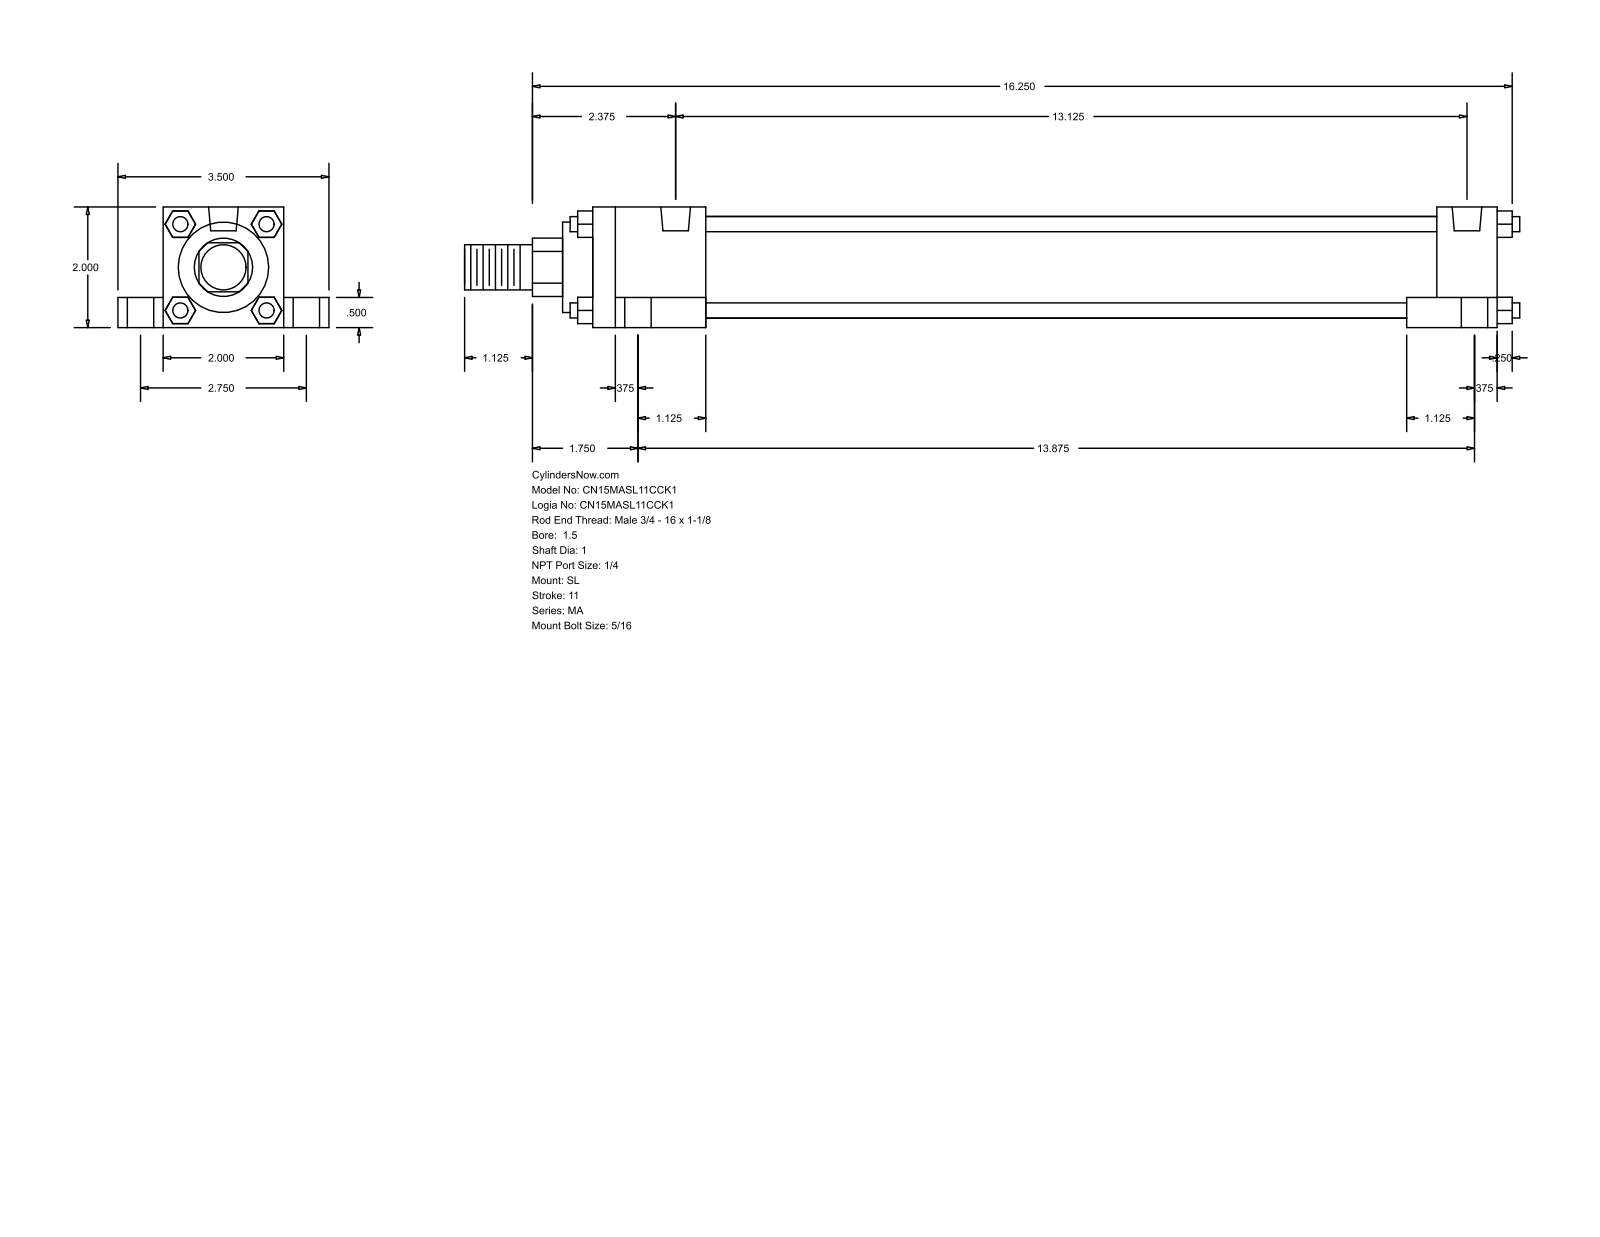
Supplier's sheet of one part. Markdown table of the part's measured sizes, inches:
| quantity | value |
| --- | --- |
| part name | MA_SL__0150_1 |
| STEP written by | GSSL Pune (CONFIG_CONTROL_DESIGN) |
| units | inches |
| bodies | 0 solids, 148 faces (112 planar, 36 cylindrical, 0 other) |
| overall size | 17.5 × 3.5 × 2 |
| round holes (diameter × count) | 0.313 × 4, 0.437 × 4, 0.687 × 4, 0.492 × 2 |
| round bosses / shafts (diameter × count) | 0.25 × 4, 1.69 × 1, 1.5 × 1, 1 × 1, 0.75 × 1 |
| partial cylindrical surfaces (radius × count) | 0.484 × 1 |
| main face-to-face distances | 2, 0.5, 0.75, 2.75, 1.5, 0.375, 15, 1, 0.25, 14 |
| hole center spacings | 1.38, 1.51, 2.75, 13.125, 13.321, 13.819, 13.875, 14.145 |
